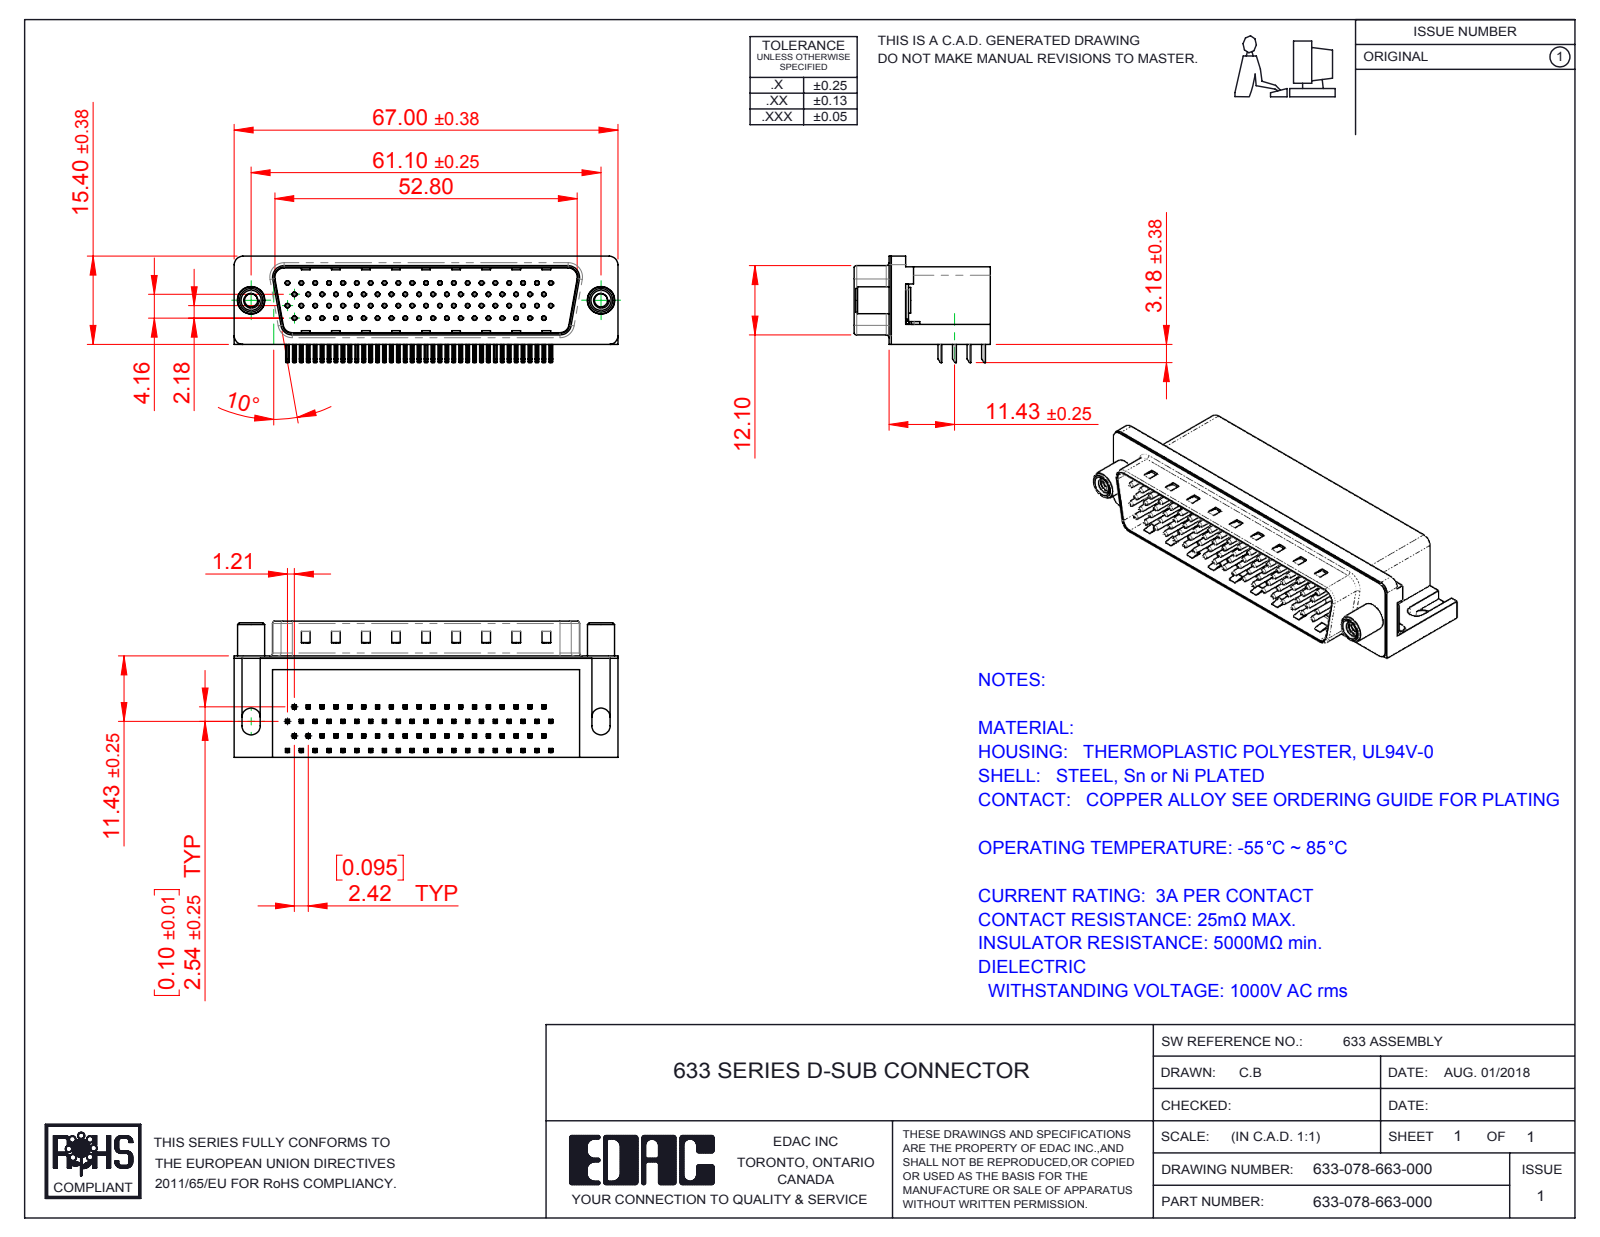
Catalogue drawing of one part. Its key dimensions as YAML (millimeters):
part_name: "633 Contact Middle_78 Contact; 633 Round Threaded Standoff; 633 Shell_78 Contact; 633 Contact Bottom_78 Contact (+5 more)"
step_written_by: "SolidWorks 2016 (CONFIG_CONTROL_DESIGN)"
units: millimeters
bodies: {solids: 84, faces: 6264, planar: 3971, cylindrical: 1782, other: 511}
overall_size: [67, 23.8, 18.58]
volume: 14655
surface_area: 16324
round_holes:
  - {diameter: 0.35, count: 78}
  - {diameter: 0.8, count: 78}
  - {diameter: 2.3, count: 2}
  - {diameter: 3.1, count: 2}
  - {diameter: 4, count: 2}
  - {diameter: 4.8, count: 2}
  - {diameter: 5, count: 2}
round_bosses_or_shafts:
  - {diameter: 0.75, count: 78}
  - {diameter: 4.9, count: 2}
  - {diameter: 4.7, count: 2}
  - {diameter: 4.5, count: 2}
  - {diameter: 3.85, count: 2}
partial_cylinders:
  - {radius: 0.25, count: 312}
  - {radius: 0.12, count: 156}
  - {radius: 1, count: 16}
  - {radius: 0.5, count: 9}
  - {radius: 1.6, count: 8}
  - {radius: 1.5, count: 6}
  - {radius: 0.45, count: 4}
  - {radius: 0.9, count: 4}
face_to_face_distances: [0.4, 13.2, 17.3, 11.7, 13.35, 2.05, 13.75, 1.65, 11.9, 1.85]
hole_center_spacings: [2.42, 4.84, 7.26, 9.68, 6.26, 7.13, 12.1, 8.62]
